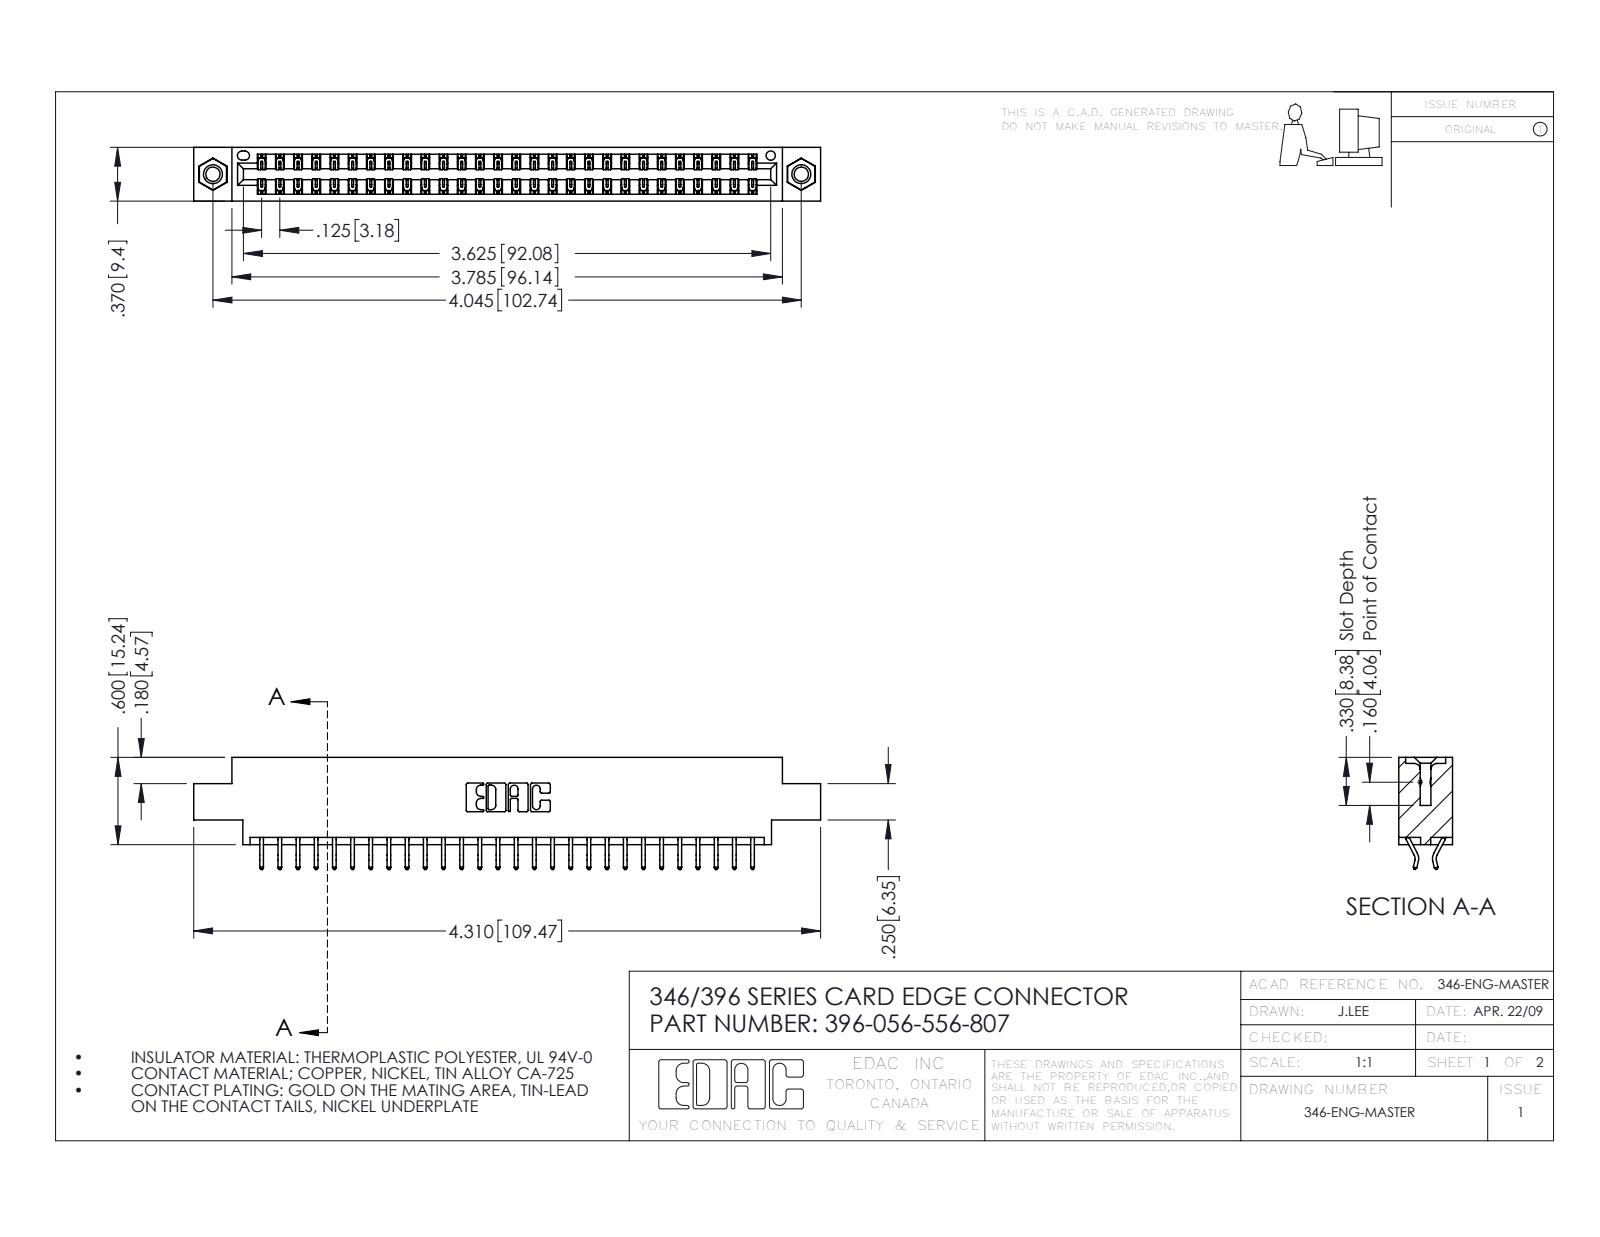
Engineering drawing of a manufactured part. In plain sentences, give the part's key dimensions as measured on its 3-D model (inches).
The part is named "396-056-556-807; 345-292-001_556 Tail; 346 Part_0.170 Offset - 0.156 Dia-TI; 345-250-001_345-250-005-103". Its 3-D file was written by "SolidWorks 2016 (CONFIG_CONTROL_DESIGN)". It is 59 solids with 3434 faces: 2296 planar, 1122 cylindrical and 16 other. Overall it measures 4.31 by 0.77 by 0.37 inches. Its volume is 0.634 cubic inches and its surface area 22.06 square inches. Round holes: 2 of diameter 0.098, 2 of diameter 0.125, 2 of diameter 0.156, 1 of diameter 0.064. Round bosses or shafts: 2 of diameter 0.155. Partial cylindrical surfaces (rounded edges, fillets, slot ends): 84 of radius 0.006, 22 of radius 0.01, 6 of radius 0.007, 6 of radius 0.031, 3 of radius 0.026, 2 of radius 0.01, 2 of radius 0.014, 2 of radius 0.022. The main face-to-face distances are 0.048, 0.322, 0.37, 0.25, 0.025, 0.072, 0.298, 0.275, 0.222, 0.148. The hole center spacings are 0.246, 3.837, 4.045.
